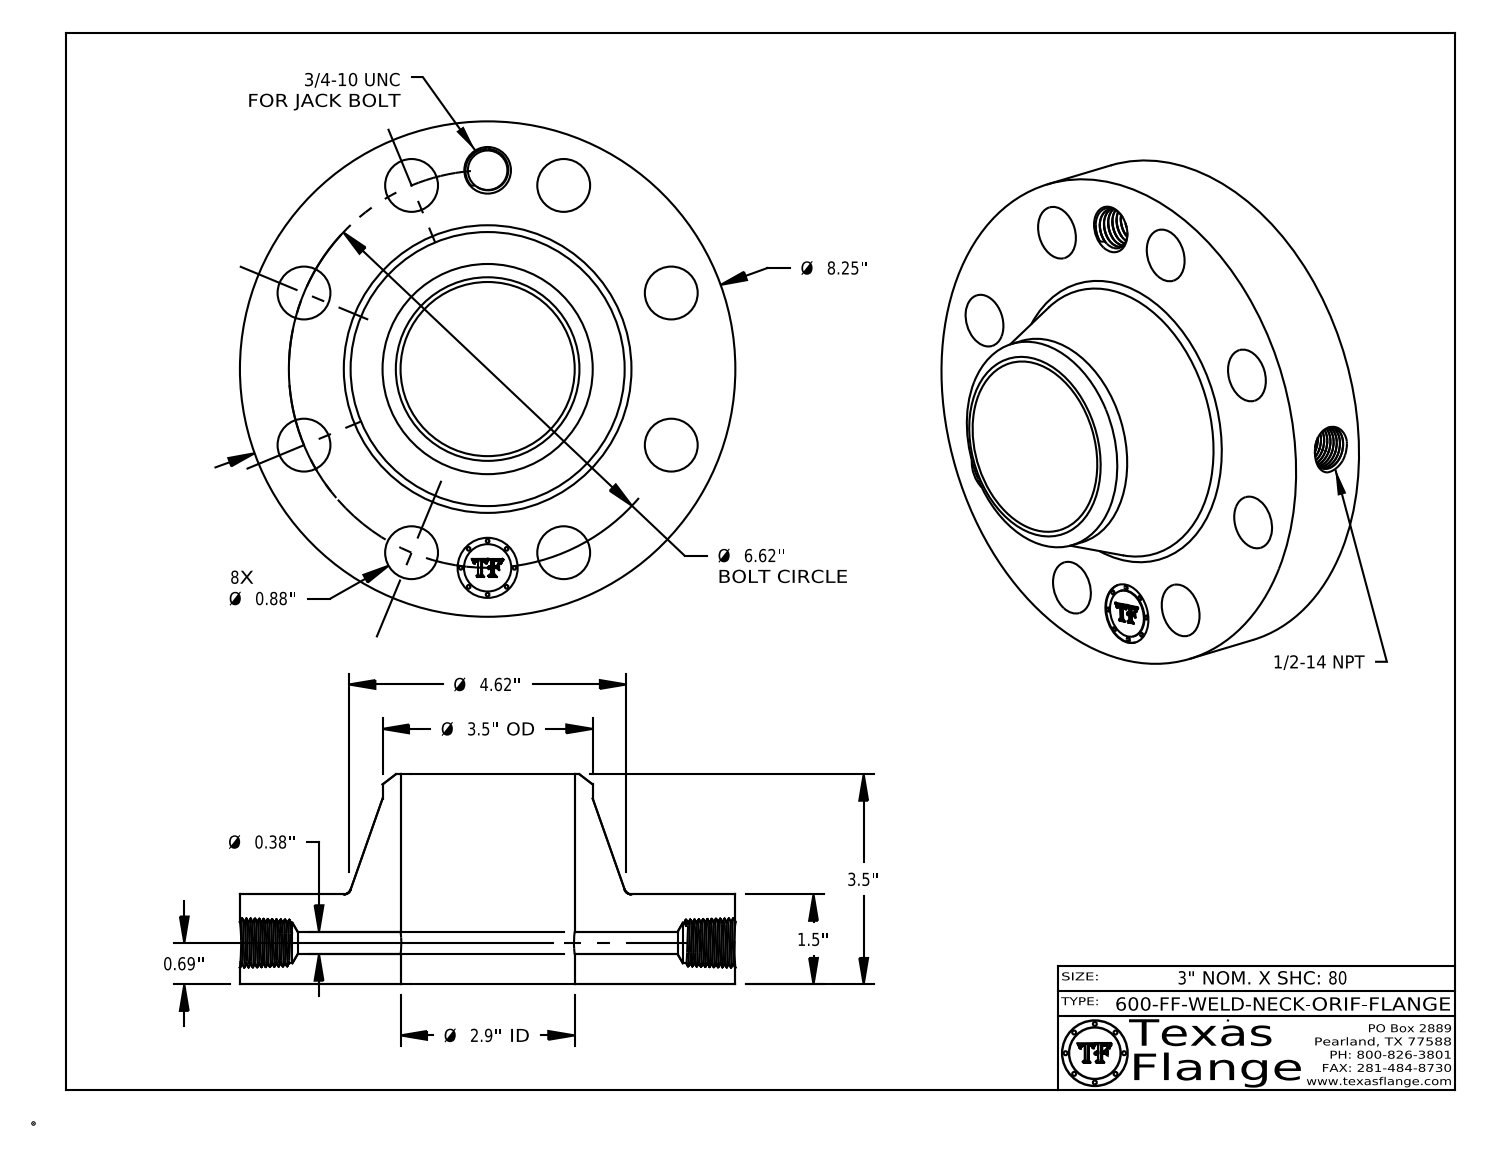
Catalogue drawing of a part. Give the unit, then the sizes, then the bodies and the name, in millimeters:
Units: millimetres
Overall size (bounding box): 209.6 × 209.6 × 88.9
Round holes (diameter × count): ⌀22.4 ×8, ⌀9.5 ×1, ⌀16.7 ×1, ⌀17.1 ×1, ⌀25.4 ×1, ⌀73.7 ×1
Round bosses / shafts (diameter × count): ⌀1.5 ×8, ⌀209.6 ×1, ⌀88.9 ×1, ⌀20 ×1
Main face-to-face distances: 38.1, 88.9, 50.8, 0.4, 37.7, 51.2, 7.6, 7.4, 1.4, 6.3
Hole centre spacings: 84.1, 118.9, 155.3, 168.1, 32.8, 64.3, 64.3, 93.4
Volume: 1 188 000 mm³ · Surface area: 141 700 mm²
Bodies: 1 solid, 766 faces (368 planar, 90 cylindrical, 308 other)
Part name (STEP PRODUCT): 600-FF-WELD-NECK
STEP written by: CATIA V5 STEP AP214 (AUTOMOTIVE_DESIGN)
